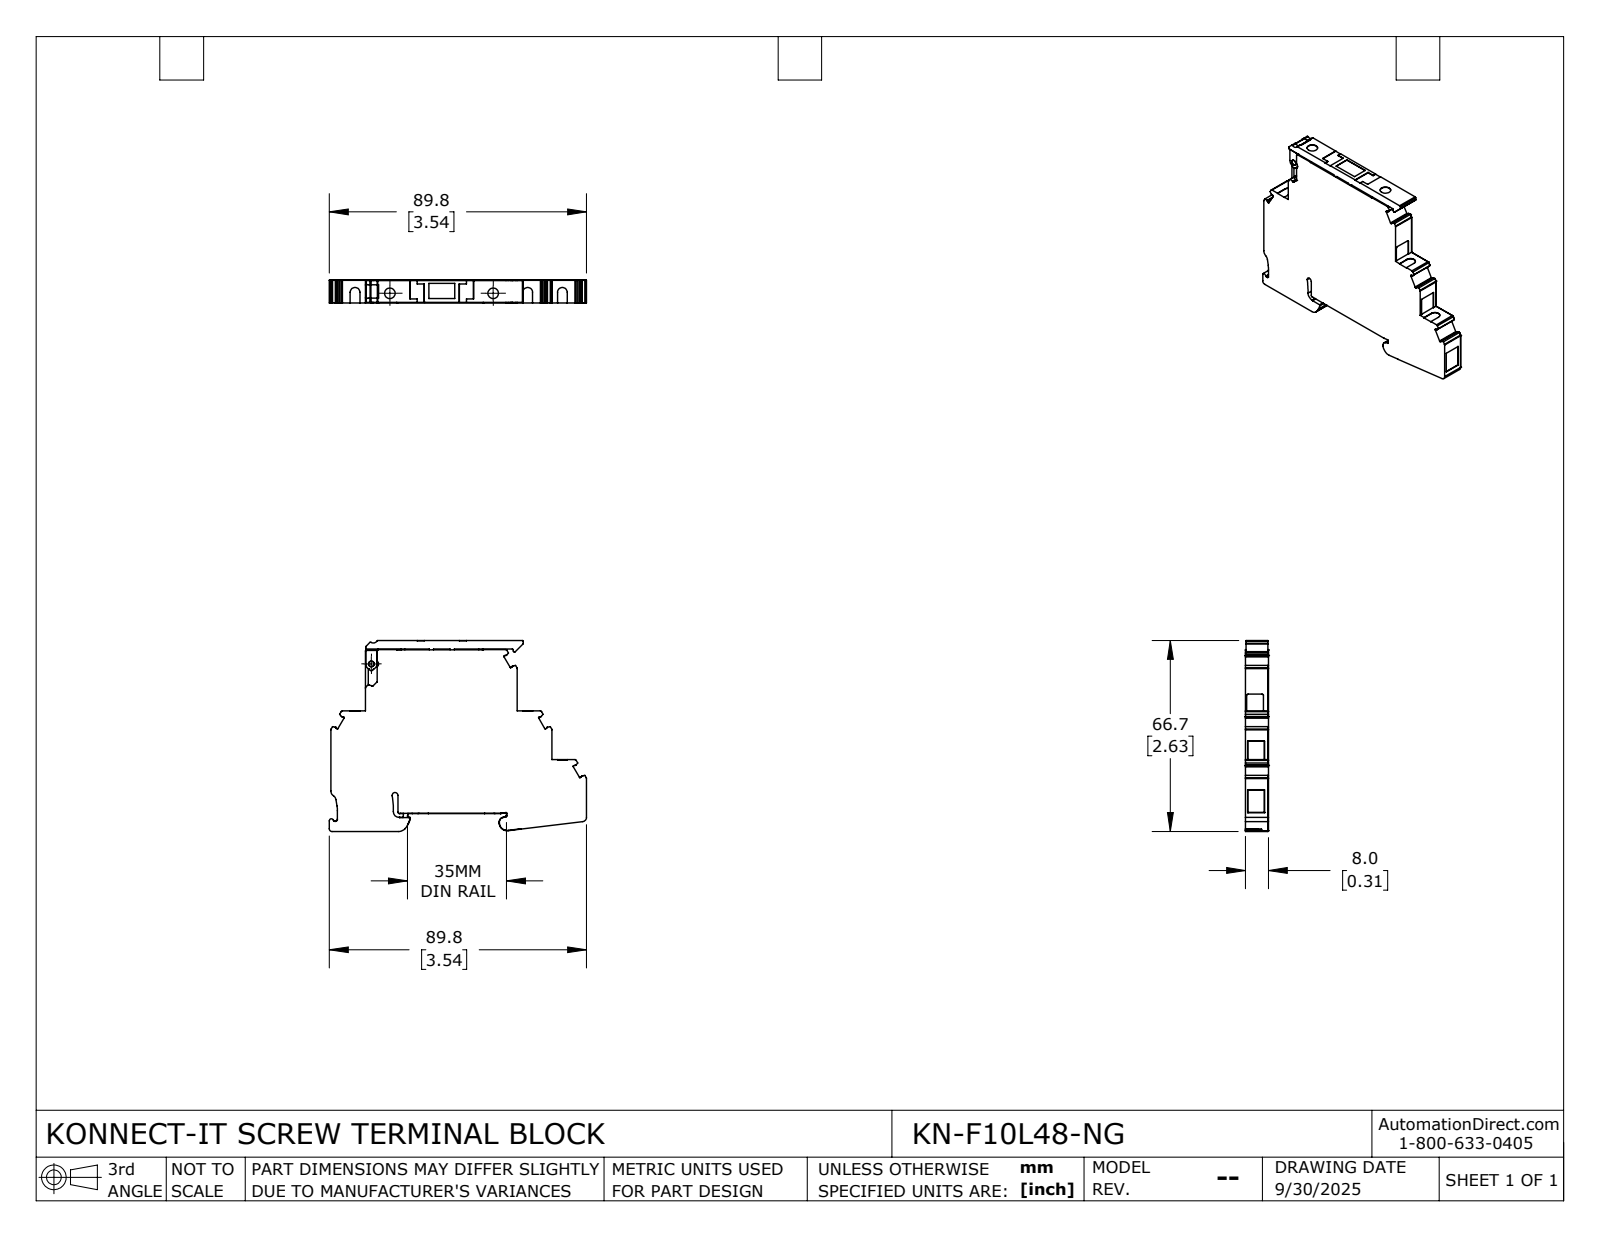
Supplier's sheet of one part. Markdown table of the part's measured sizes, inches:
| quantity | value |
| --- | --- |
| part name | KN-F10L48-NG |
| STEP written by | SolidWorks 2024 (CONFIG_CONTROL_DESIGN) |
| units | inches |
| bodies | 1 solid, 530 faces (292 planar, 233 cylindrical, 5 other) |
| overall size | 3.537 × 2.626 × 0.315 |
| volume | 2.159 in³ |
| surface area | 19.86 in² |
| round holes (diameter × count) | 0.146 × 2, 0.169 × 2, 0.079 × 1 |
| round bosses / shafts (diameter × count) | 0.075 × 1 |
| partial cylindrical surfaces (radius × count) | 0.02 × 31, 0.012 × 29, 0.016 × 17, 0.004 × 9, 0.01 × 8, 0.008 × 6, 0.039 × 6, 0.035 × 3 |
| main face-to-face distances | 0.315, 0.307, 0.476, 2.25, 0.13, 0.126, 0.118, 2.376, 2.261, 0.114 |
| hole center spacings | 1.421, 1.419, 1.423 |
